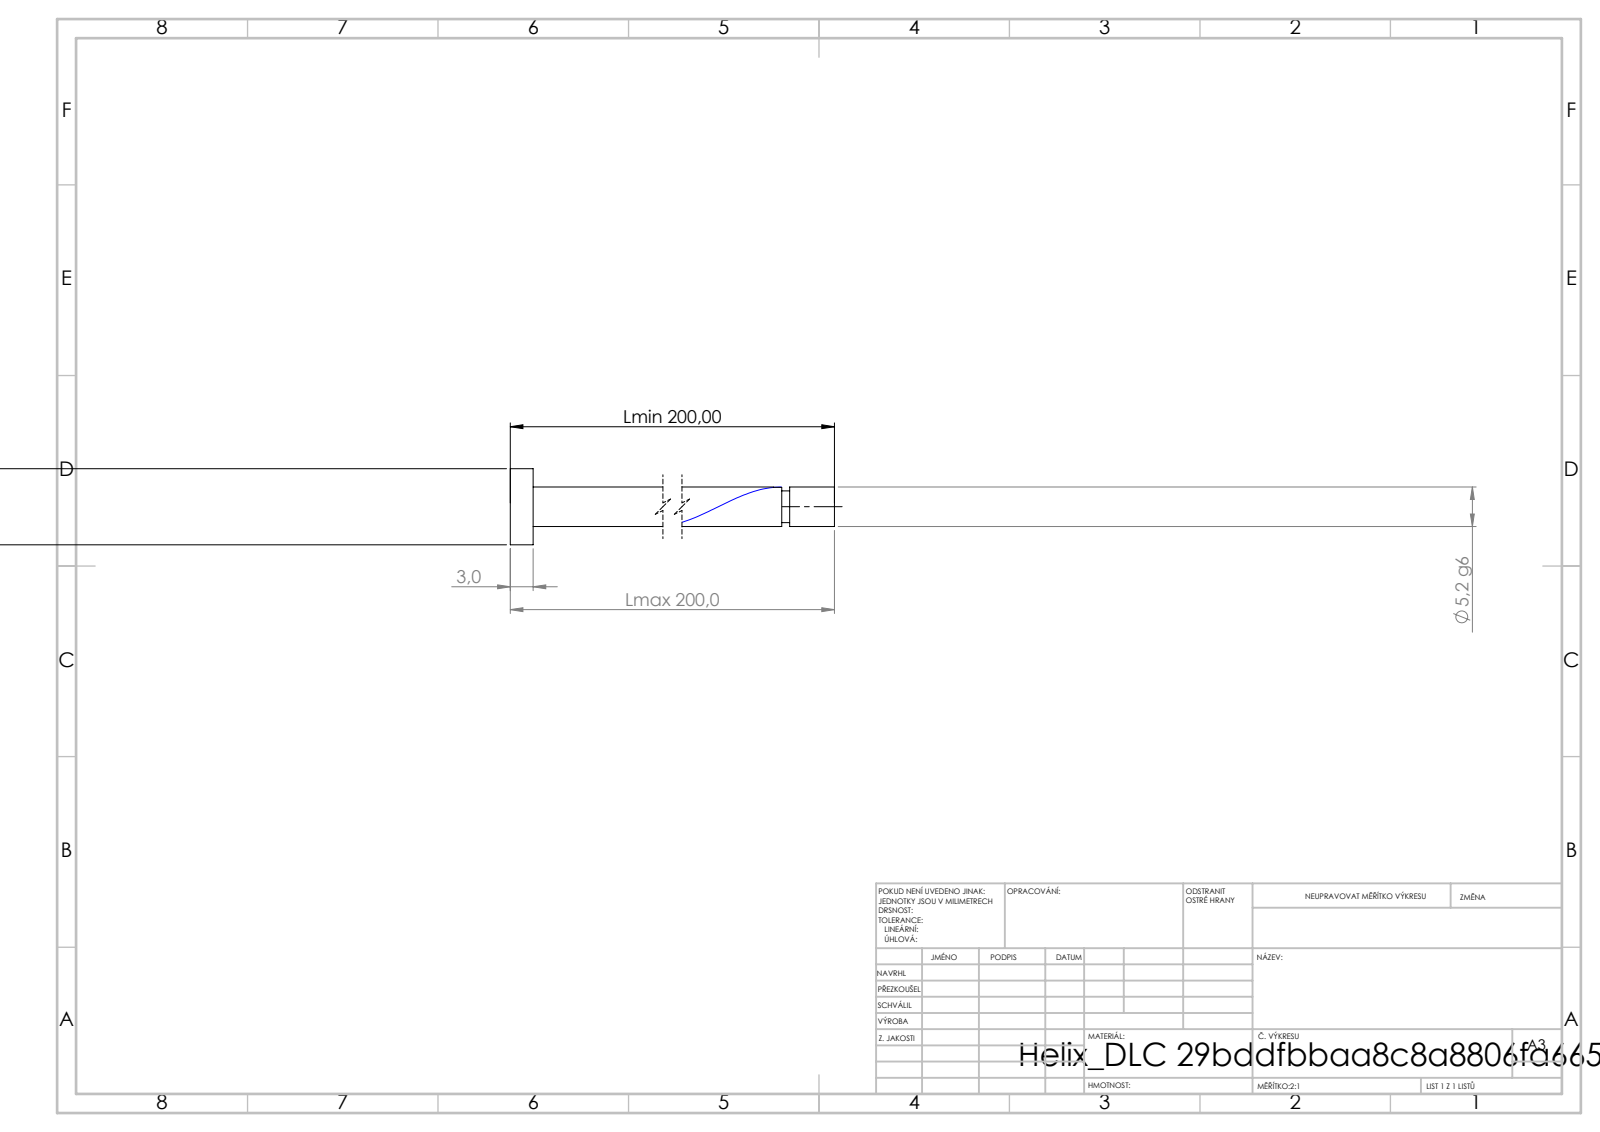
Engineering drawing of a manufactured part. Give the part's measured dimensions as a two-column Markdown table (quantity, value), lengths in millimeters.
| quantity | value |
| --- | --- |
| STEP written by | SolidWorks 2019 (CONFIG_CONTROL_DESIGN) |
| units | millimeters |
| bodies | 1 solid, 21 faces (6 planar, 14 cylindrical, 1 other) |
| overall size | 200 × 10 × 10 |
| volume | 4 371 mm³ |
| surface area | 3 538 mm² |
| round bosses / shafts (diameter × count) | 10 × 1, 5.2 × 1, 4.16 × 1 |
| main face-to-face distances | 3, 200, 197, 194.12, 191.12, 5.88, 193.08, 190.08, 1.04, 6.92 |
